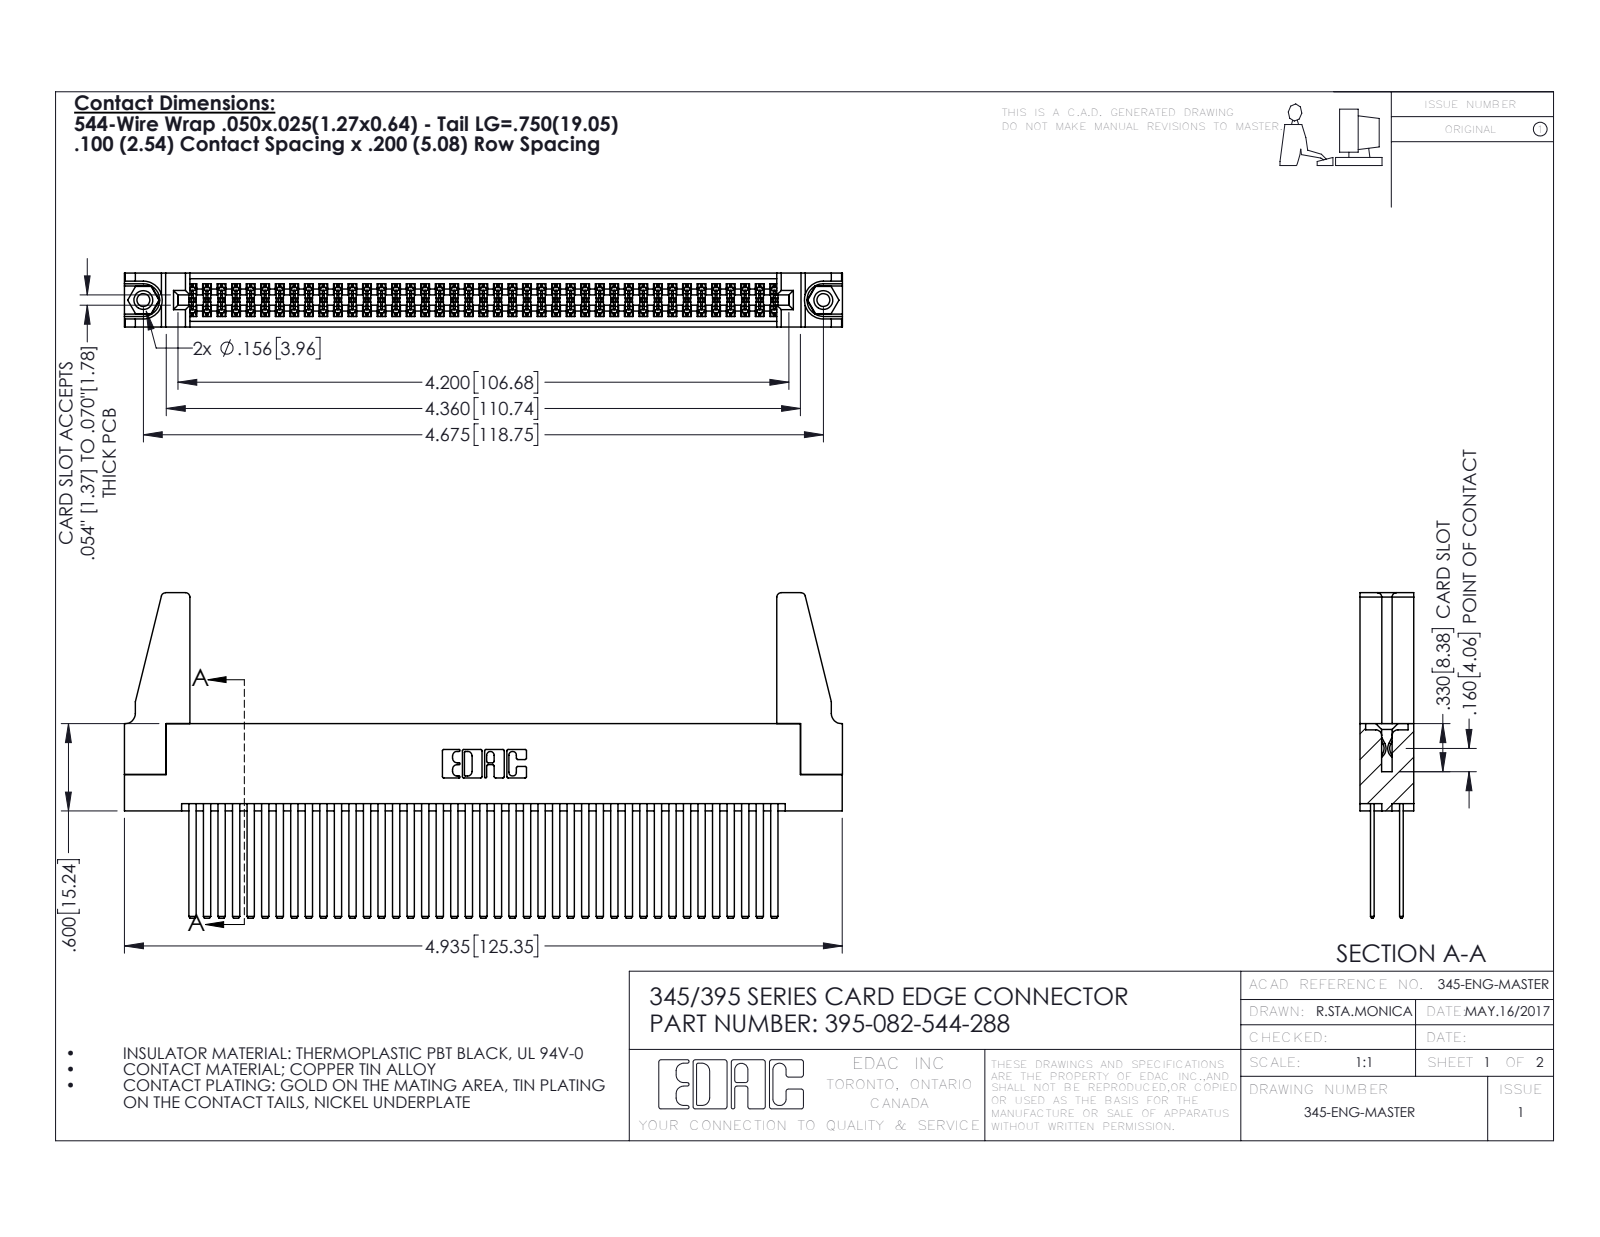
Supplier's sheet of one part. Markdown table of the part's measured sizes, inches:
| quantity | value |
| --- | --- |
| part name | 345-220-078_345-220-088; 345-250-001_345-250-001-102; 345-292-001_345-293-144; 395-082-544-288 (+1 more) |
| STEP written by | SolidWorks 2016 (CONFIG_CONTROL_DESIGN) |
| units | inches |
| bodies | 87 solids, 3858 faces (2530 planar, 1312 cylindrical, 16 other) |
| overall size | 4.936 × 2.237 × 0.37 |
| volume | 1.011 in³ |
| surface area | 40.55 in² |
| round holes (diameter × count) | 0.089 × 2, 0.125 × 2, 0.156 × 2, 0.064 × 1 |
| round bosses / shafts (diameter × count) | 0.155 × 2 |
| partial cylindrical surfaces (radius × count) | 0.006 × 123, 0.01 × 22, 0.03 × 8, 0.007 × 6, 0.031 × 6, 0.026 × 3, 0.014 × 2, 0.019 × 2 |
| main face-to-face distances | 0.072, 0.298, 0.2, 0.098, 0.272, 0.025, 0.225, 0.37, 0.175, 0.149 |
| hole center spacings | 0.27, 4.439, 4.675 |
